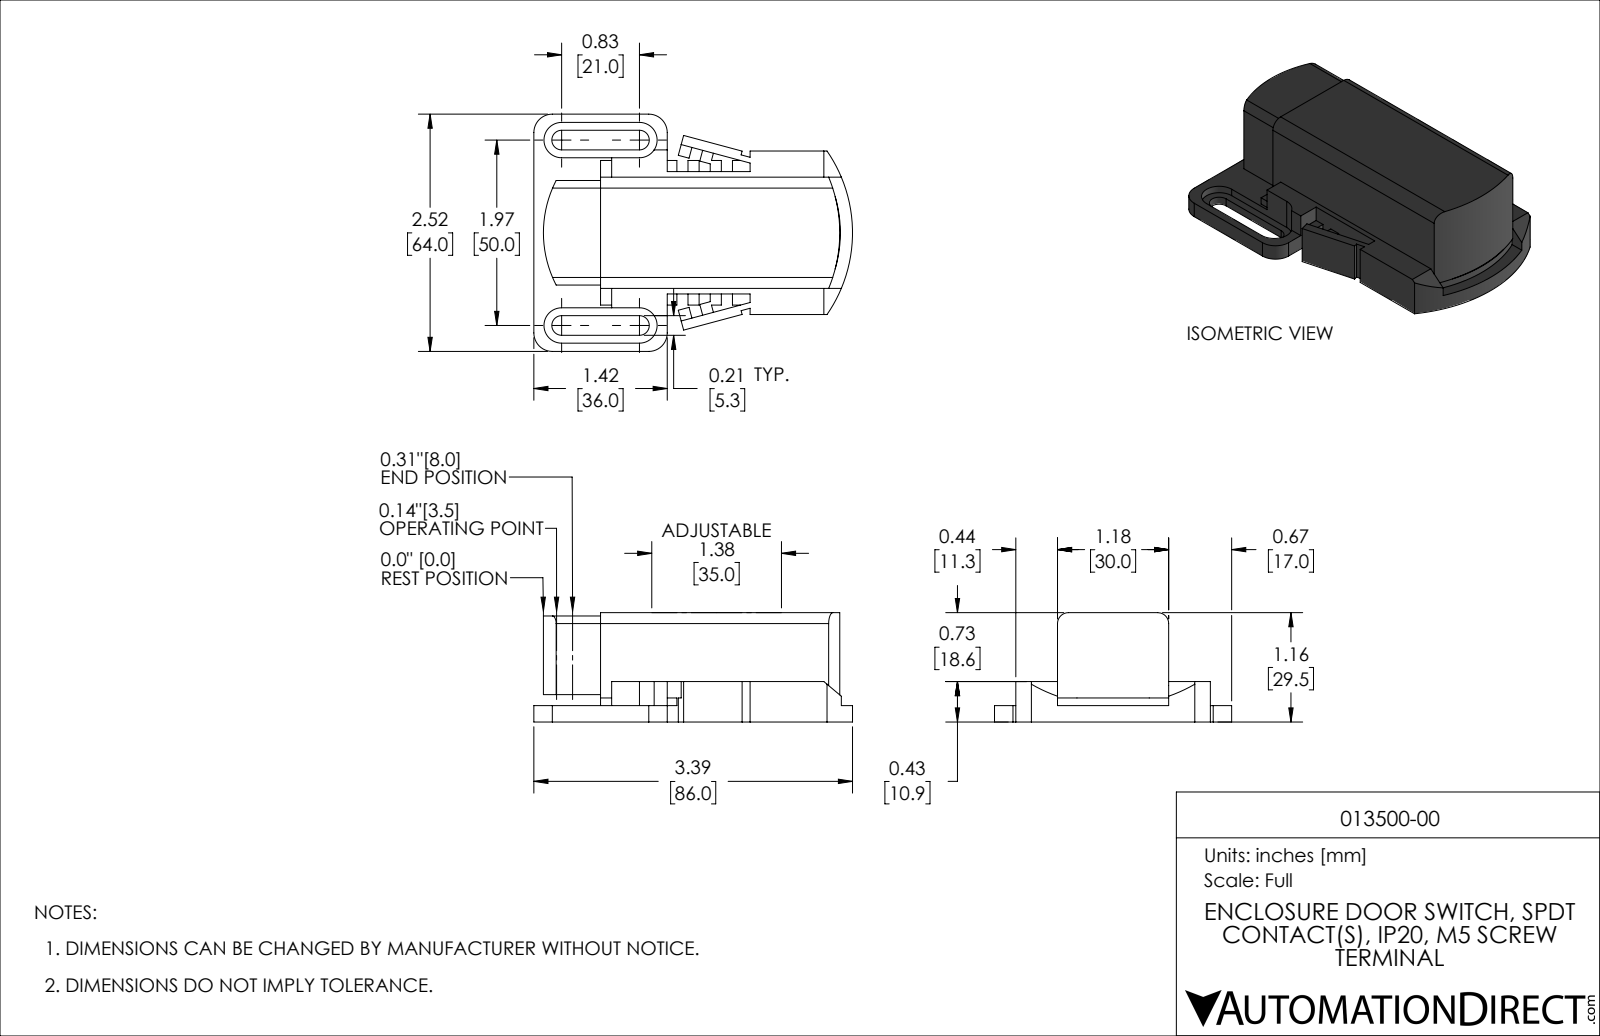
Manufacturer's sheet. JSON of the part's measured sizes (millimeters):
{"part_name": "PRODUCT_NAME_1", "step_written_by": "ACIS (AUTOMOTIVE_DESIGN_CC2)", "units": "millimeters", "bodies": {"solids": 1, "faces": 135, "planar": 111, "cylindrical": 24, "other": 0}, "overall_size": [86, 64, 29.5], "volume_mm3": 77754, "surface_area_mm2": 17225, "partial_cylinders_radius": [[2.65, 4], [4.77, 4], [4.98, 4], [2.05, 2], [2.95, 2], [30.62, 1], [34.69, 1], [38.77, 1]], "face_to_face_distances": [29.5, 4.42, 25.08, 30, 0.9, 6.49, 10.91, 18.59, 22.11, 5.55]}
